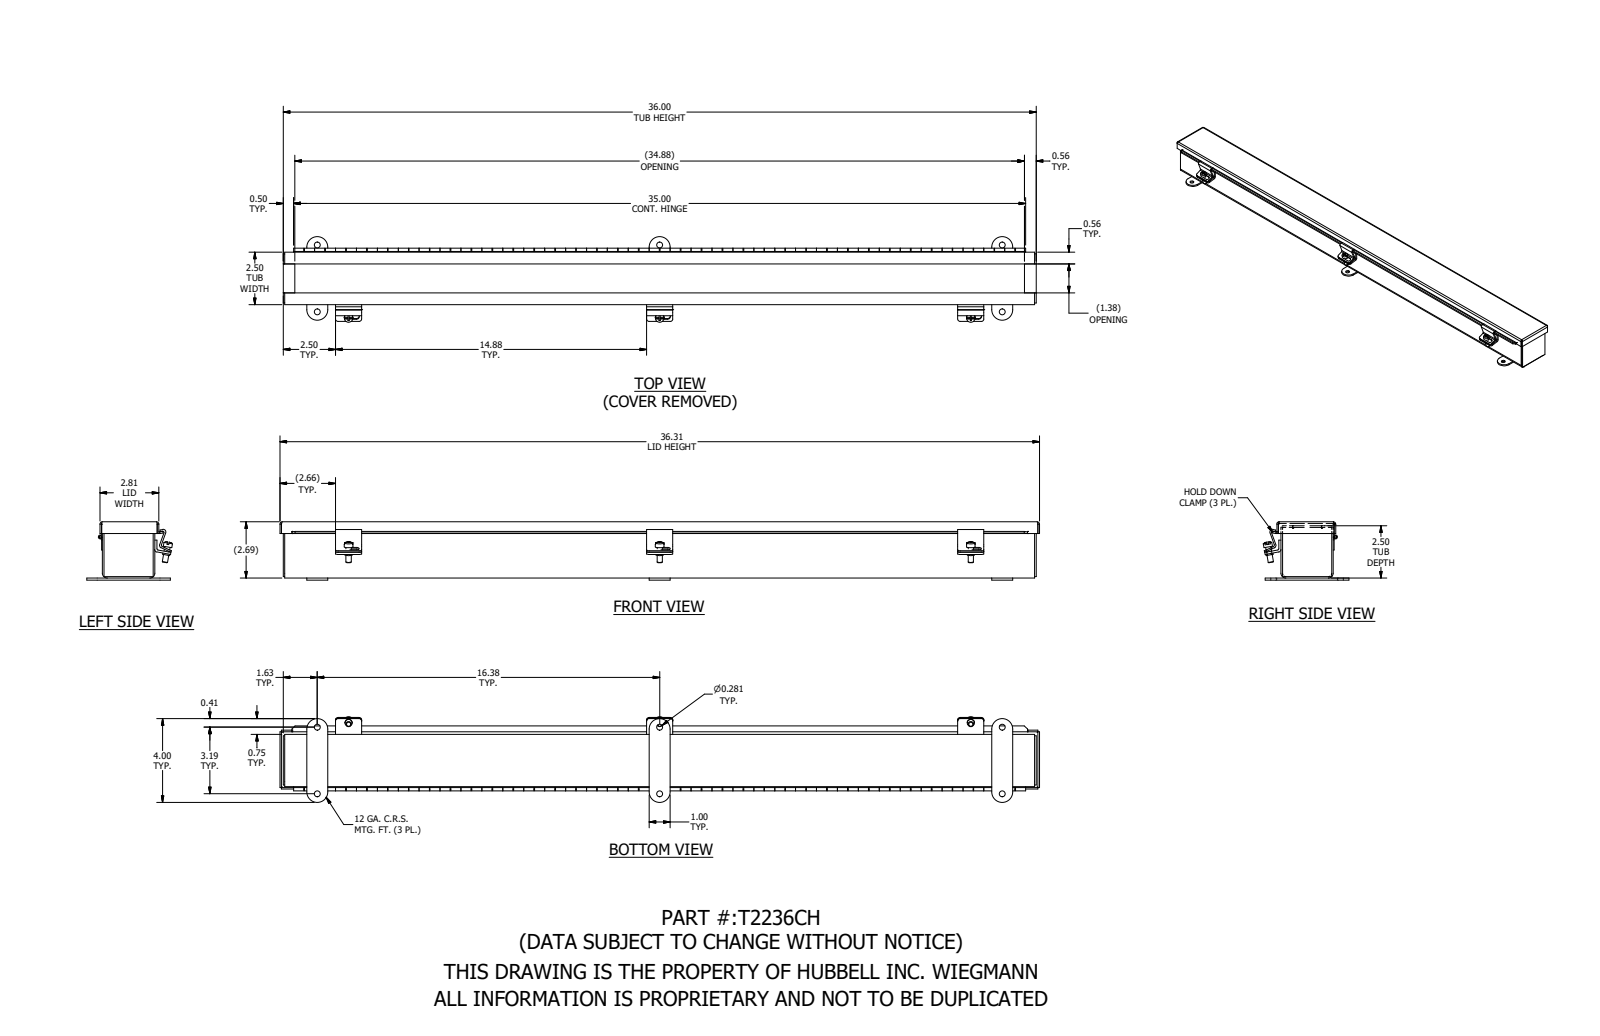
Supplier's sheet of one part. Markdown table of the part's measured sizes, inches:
| quantity | value |
| --- | --- |
| part name | T2236CH |
| STEP written by | SolidWorks 2021 (AUTOMOTIVE_DESIGN) |
| units | inches |
| bodies | 19 solids, 825 faces (414 planar, 388 cylindrical, 23 other) |
| overall size | 36.313 × 4.095 × 2.783 |
| volume | 37.64 in³ |
| surface area | 1 082 in² |
| round holes (diameter × count) | 0.281 × 6, 0.196 × 3, 0.116 × 1 |
| round bosses / shafts (diameter × count) | 0.41 × 3, 0.344 × 3, 0.25 × 3, 0.2 × 1, 0.1 × 1 |
| partial cylindrical surfaces (radius × count) | 0.125 × 12, 0.031 × 9, 0.105 × 9, 0.133 × 6, 0.5 × 6, 0.063 × 3, 0.126 × 3, 0.156 × 2 |
| main face-to-face distances | 0.074, 2.426, 2.615, 2.5, 2.352, 2.689, 2.541, 2.542, 0.116, 0.189 |
| hole center spacings | 3.187, 16.375, 16.375, 16.682, 16.683, 32.75, 32.905, 14.875 |
